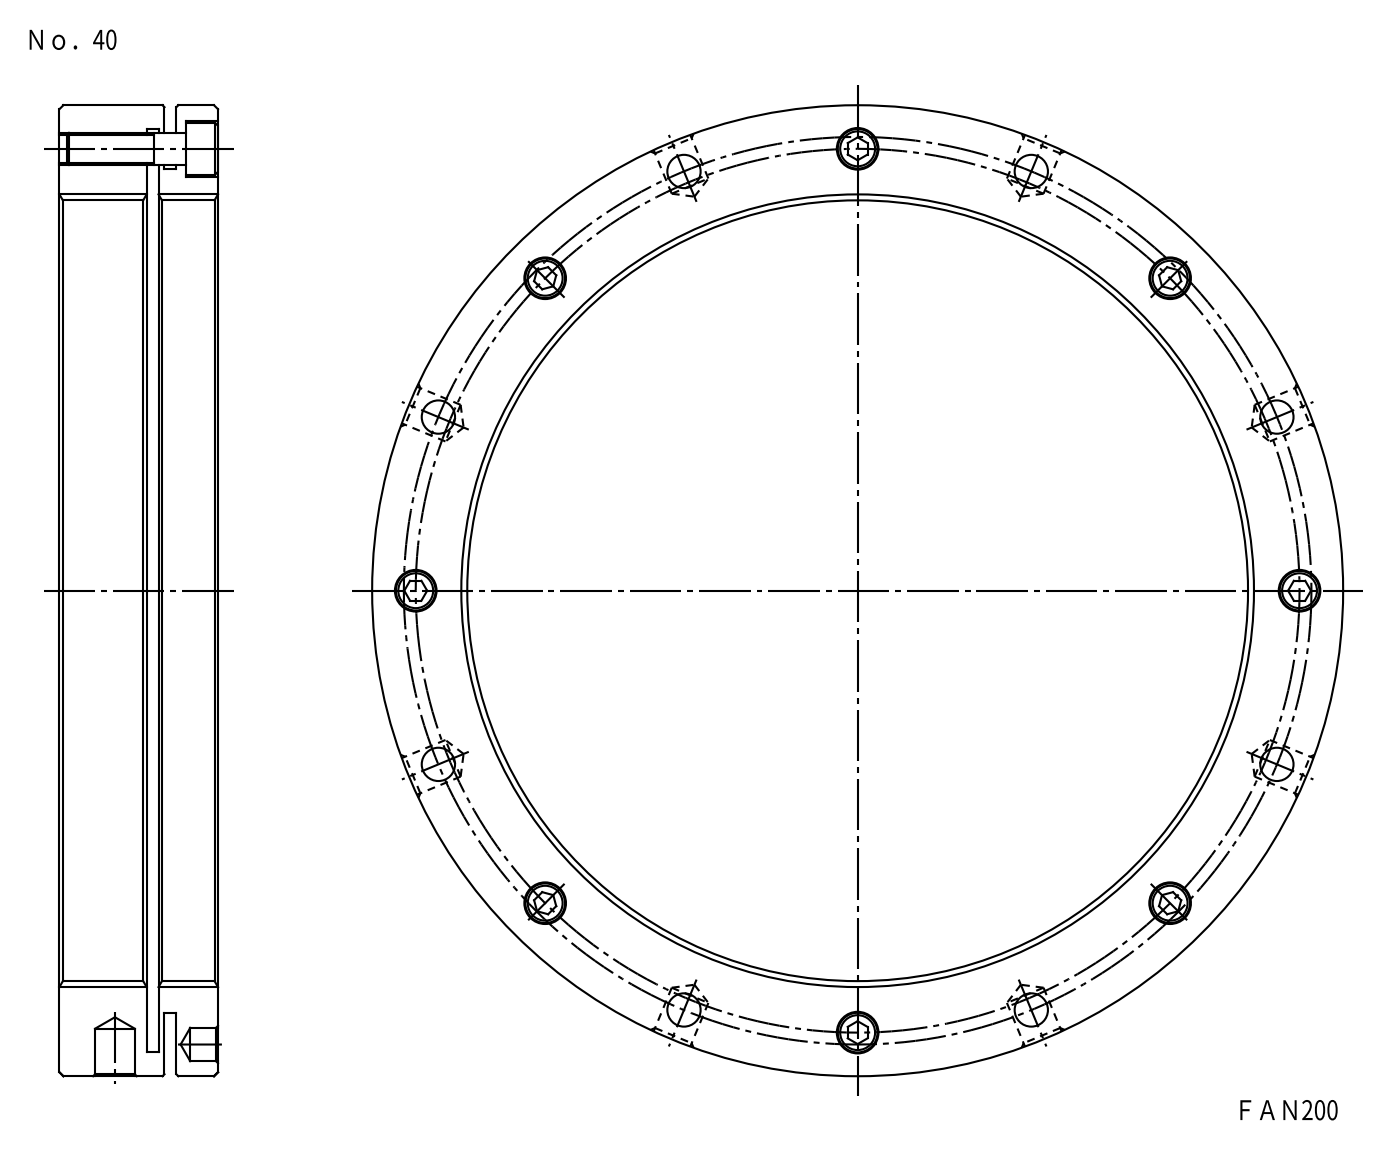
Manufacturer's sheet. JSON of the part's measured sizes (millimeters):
{"part_name": "FKD FAN200; M8X30_default", "step_written_by": "SolidWorks 2012 (CONFIG_CONTROL_DESIGN)", "units": "millimeters", "bodies": {"solids": 9, "faces": 266, "planar": 94, "cylindrical": 140, "other": 32}, "overall_size": [245, 245, 40], "volume_mm3": 550940, "surface_area_mm2": 153900, "round_holes": [[8.4, 8], [8.6, 8], [10, 8], [14, 8], [6.65, 5], [6.65, 3], [200, 1], [233, 1]], "round_bosses_or_shafts": [[13, 8], [8, 8], [245, 1], [213, 1]], "face_to_face_distances": [3, 4.5, 40, 26.5, 13.5, 29.5, 10.5, 22, 7.5, 18], "hole_center_spacings": [125.58, 221.65, 44.18, 44.19, 85.34, 111.5, 114.5, 157.68]}
